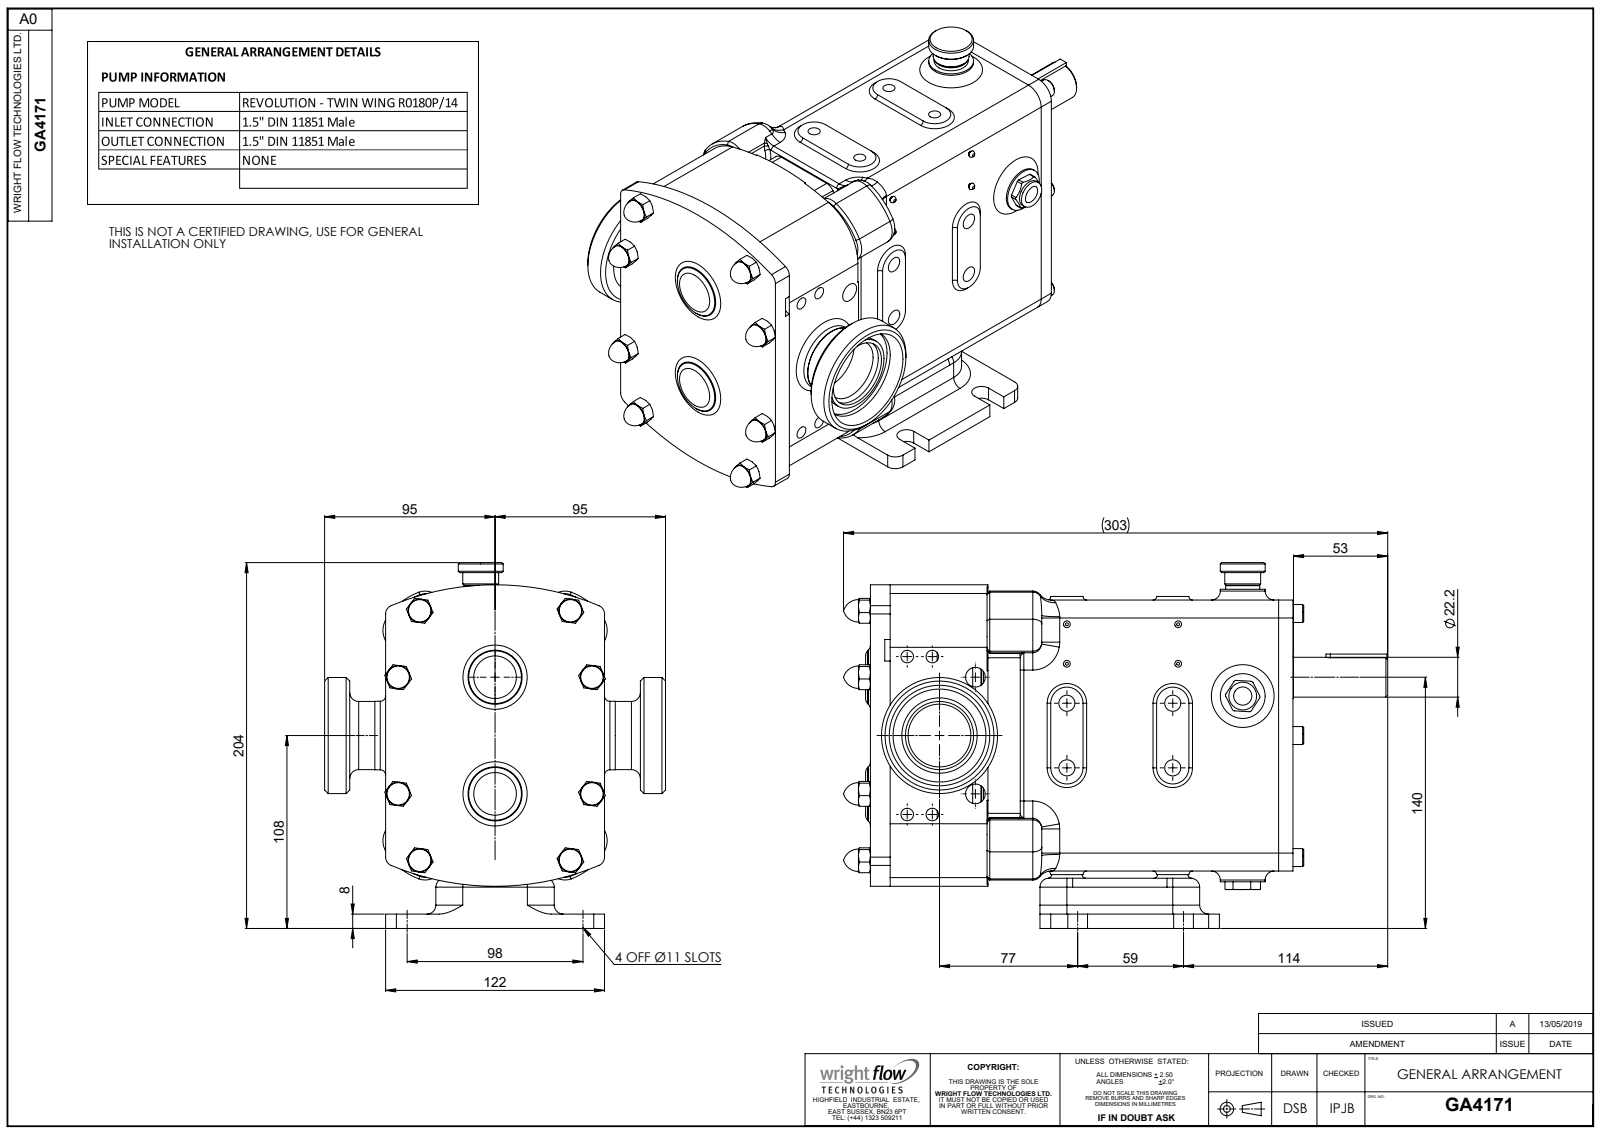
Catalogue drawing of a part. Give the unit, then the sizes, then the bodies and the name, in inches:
Units: inches
Overall size (bounding box): 11.941 × 8.026 × 7.48
Round holes (diameter × count): ⌀0.268 ×4, ⌀0.276 ×4, ⌀0.354 ×4, ⌀0.433 ×2, ⌀0.887 ×1, ⌀1.378 ×1, ⌀1.496 ×1, ⌀2.039 ×1
Round bosses / shafts (diameter × count): ⌀0.394 ×6, ⌀0.984 ×4, ⌀0.512 ×4, ⌀2.547 ×1, ⌀1.654 ×1, ⌀1.504 ×1, ⌀0.985 ×1, ⌀0.874 ×1
Partial cylindrical surfaces — rounded edges, fillets, slot ends (radius × count): R0.079 ×28, R0.394 ×26, R0.197 ×19, R0.236 ×14, R0.315 ×8, R0.05 ×6, R0.049 ×4, R0.217 ×4
Main face-to-face distances: 3.386, 0.709, 9.272, 4.094, 0.236, 0.945, 0.079, 7.205, 5.945, 4.803
Hole centre spacings: 1.417, 2.323, 2.721, 0.551, 1.048, 1.502, 1.563, 1.739
Volume: 226.8 in³ · Surface area: 390.9 in²
Bodies: 3 solids, 1239 faces (379 planar, 333 cylindrical, 527 other)
Part name (STEP PRODUCT): Copy of Z94-5031-22 - 1.5 INCH DIN11851^GA4171; GA4171; Copy of R0180 CPP H TSD^GA4171
STEP written by: SolidWorks 2023 (AUTOMOTIVE_DESIGN)
